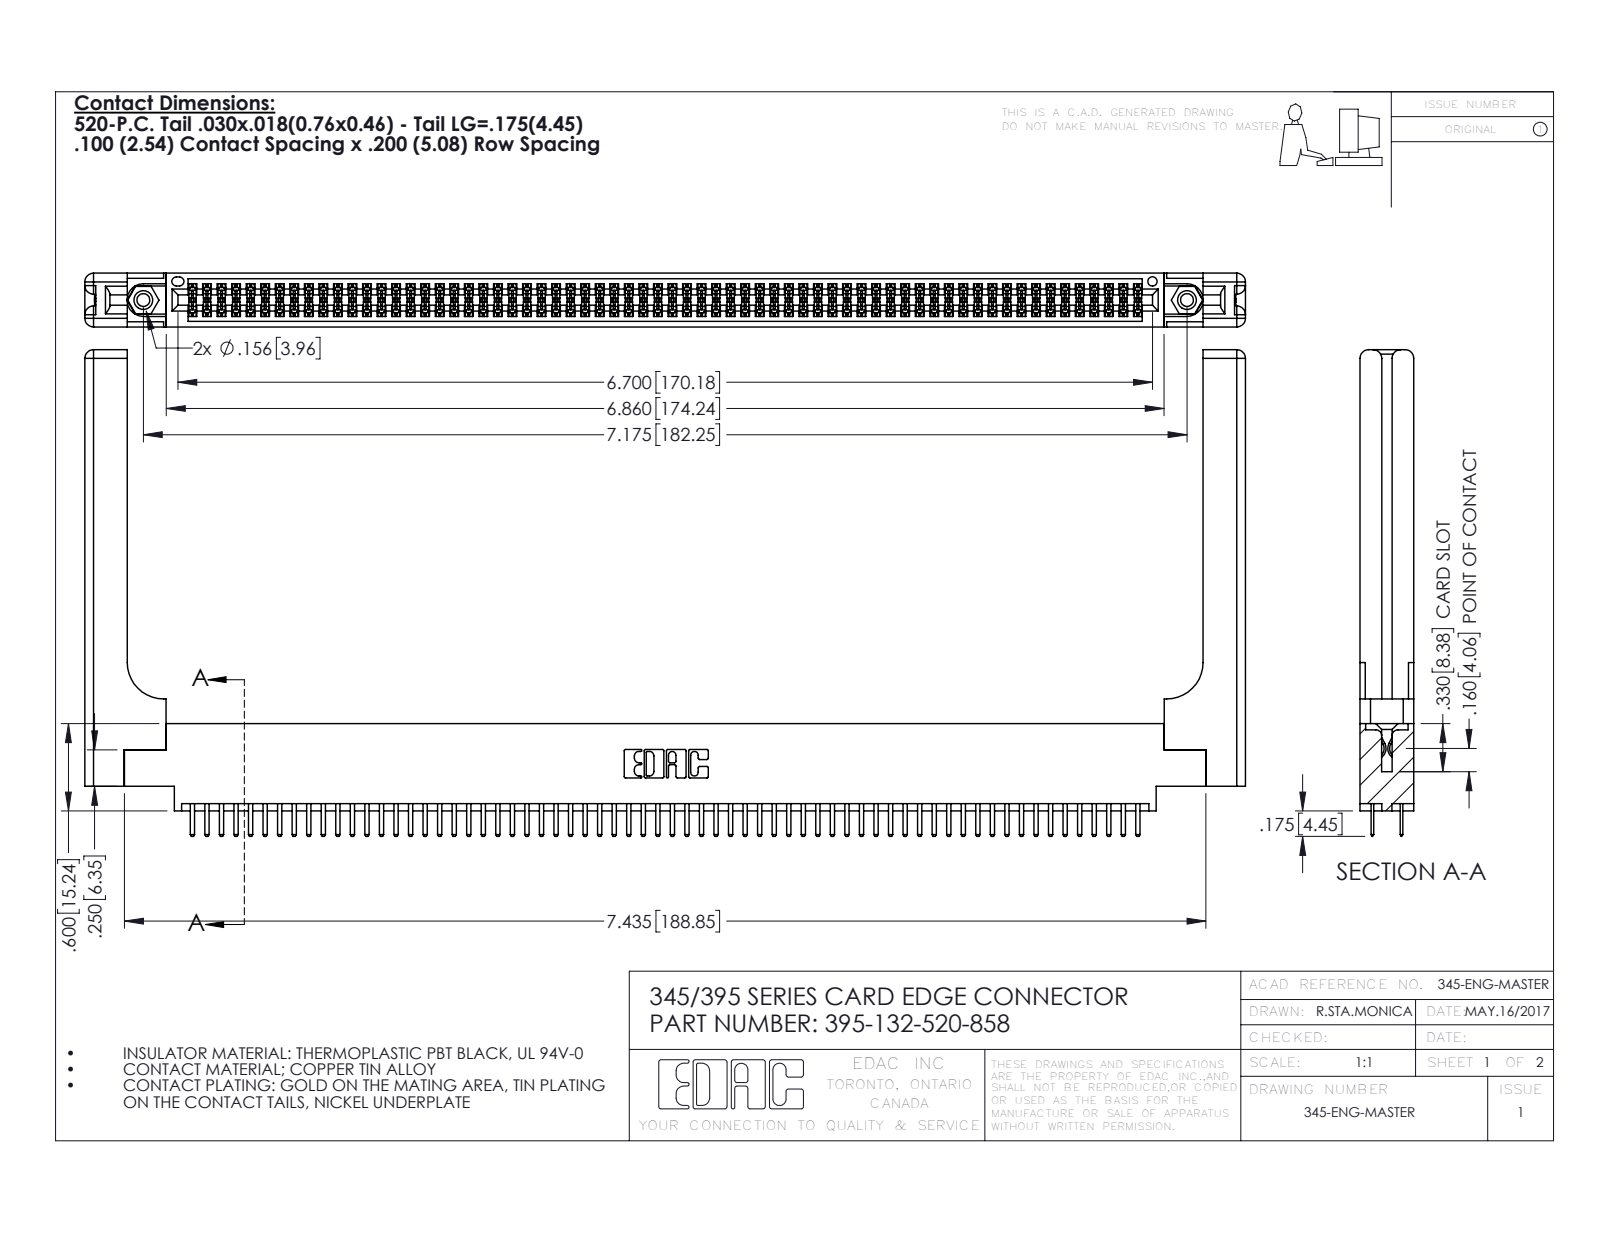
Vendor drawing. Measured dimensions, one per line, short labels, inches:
name: 345 Part_0.170 Offset - 0.156 Dia-TH; 395-132-520-858; 345-292-001_345-293-120; 345-220-058_345-220-058 (+1 more)
written by: SolidWorks 2016 (CONFIG_CONTROL_DESIGN)
unit: in
bodies: 137 solids, 7514 faces (4852 planar, 2602 cylindrical, 60 other)
size: 7.979 × 3.345 × 0.37
volume: 1.722 in³; area: 53.82 in²
holes: 2× ⌀0.089, 2× ⌀0.125, 2× ⌀0.156, 1× ⌀0.064
bosses: 2× ⌀0.155
rounds: 198× R0.006, 136× R0.01, 22× R0.01, 16× R0.06, 6× R0.007, 6× R0.031, 3× R0.026, 2× R0.014
face distances: 0.072, 0.37, 0.298, 0.2, 0.098, 0.272, 0.025, 0.225, 0.022, 0.175
hole spacings: 0.27, 6.939, 7.175
